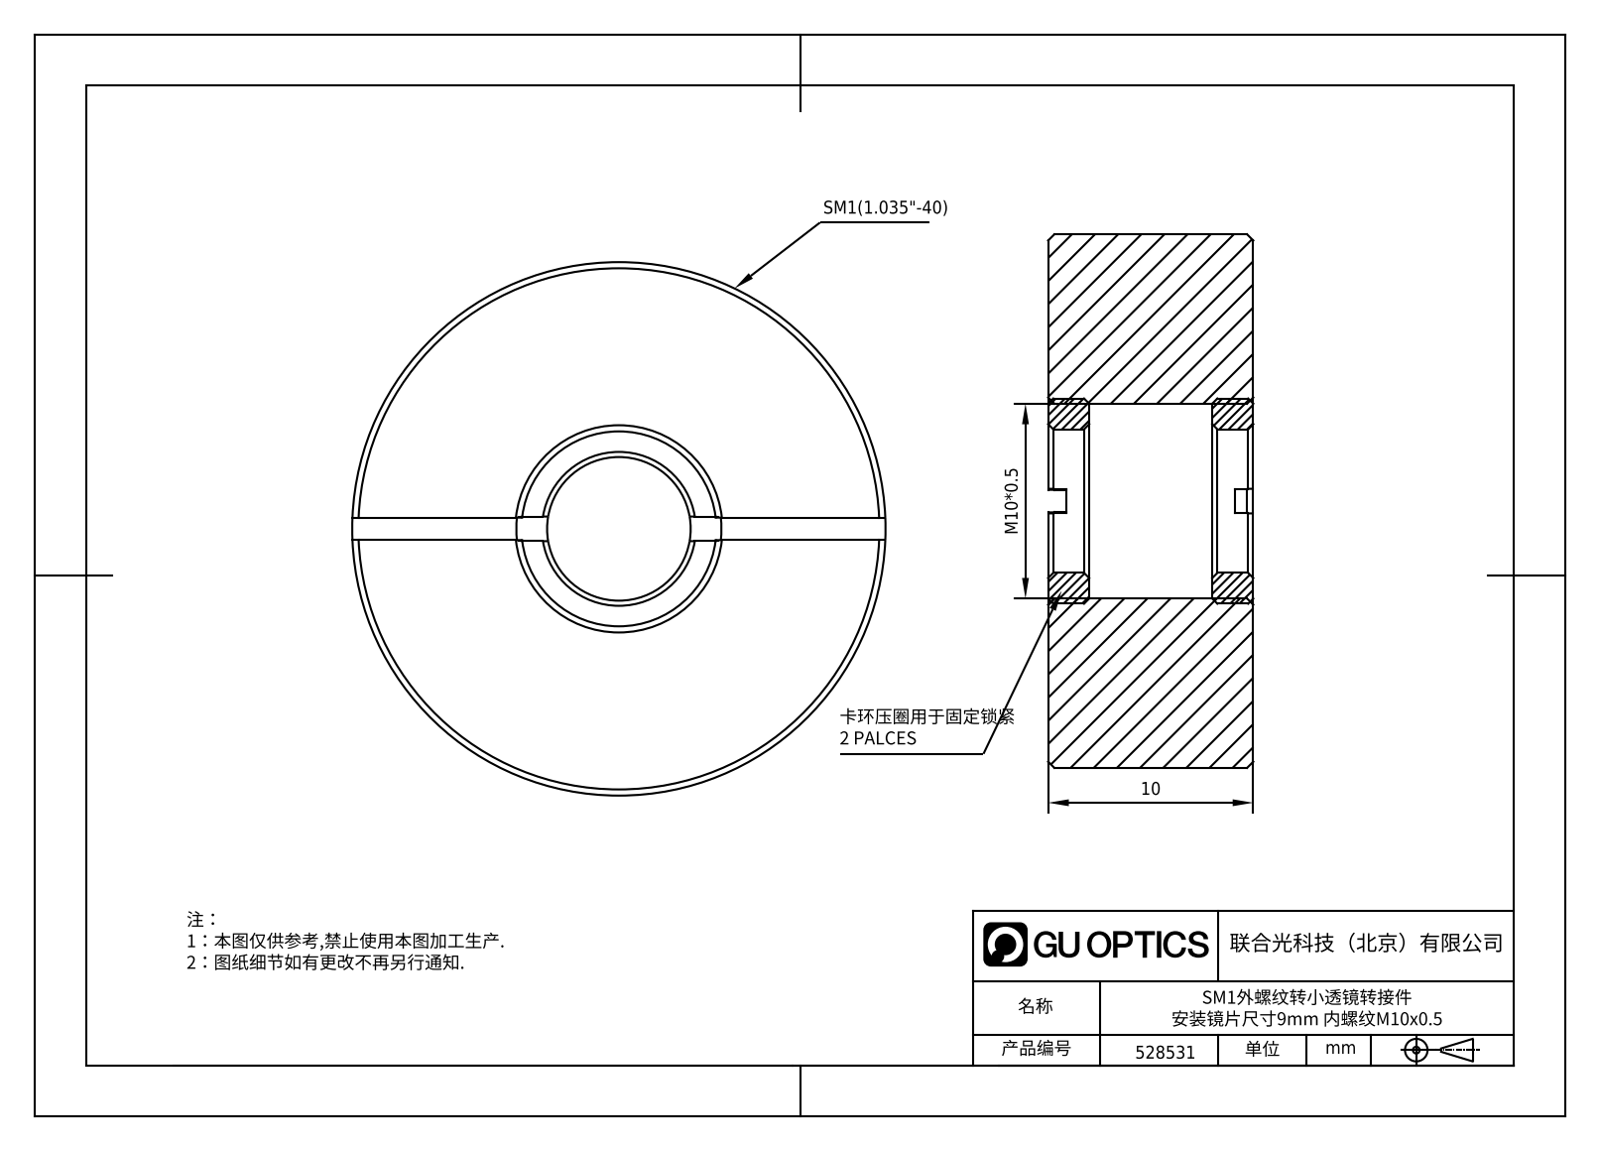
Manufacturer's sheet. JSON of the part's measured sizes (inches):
{"part_name": "528531", "step_written_by": "SolidWorks 2020 (CONFIG_CONTROL_DESIGN)", "units": "inches", "bodies": {"solids": 3, "faces": 51, "planar": 27, "cylindrical": 6, "other": 18}, "overall_size": [1.024, 1.024, 0.394], "volume_in3": 0.288, "surface_area_in2": 3.675, "round_holes": [[0.276, 1], [0.374, 1]], "round_bosses_or_shafts": [[1.024, 1], [0.394, 1]], "face_to_face_distances": [0.394, 0.079, 0.315, 0.039, 0.236, 0.043, 0.354, 0.276, 0.045, 0.035]}
